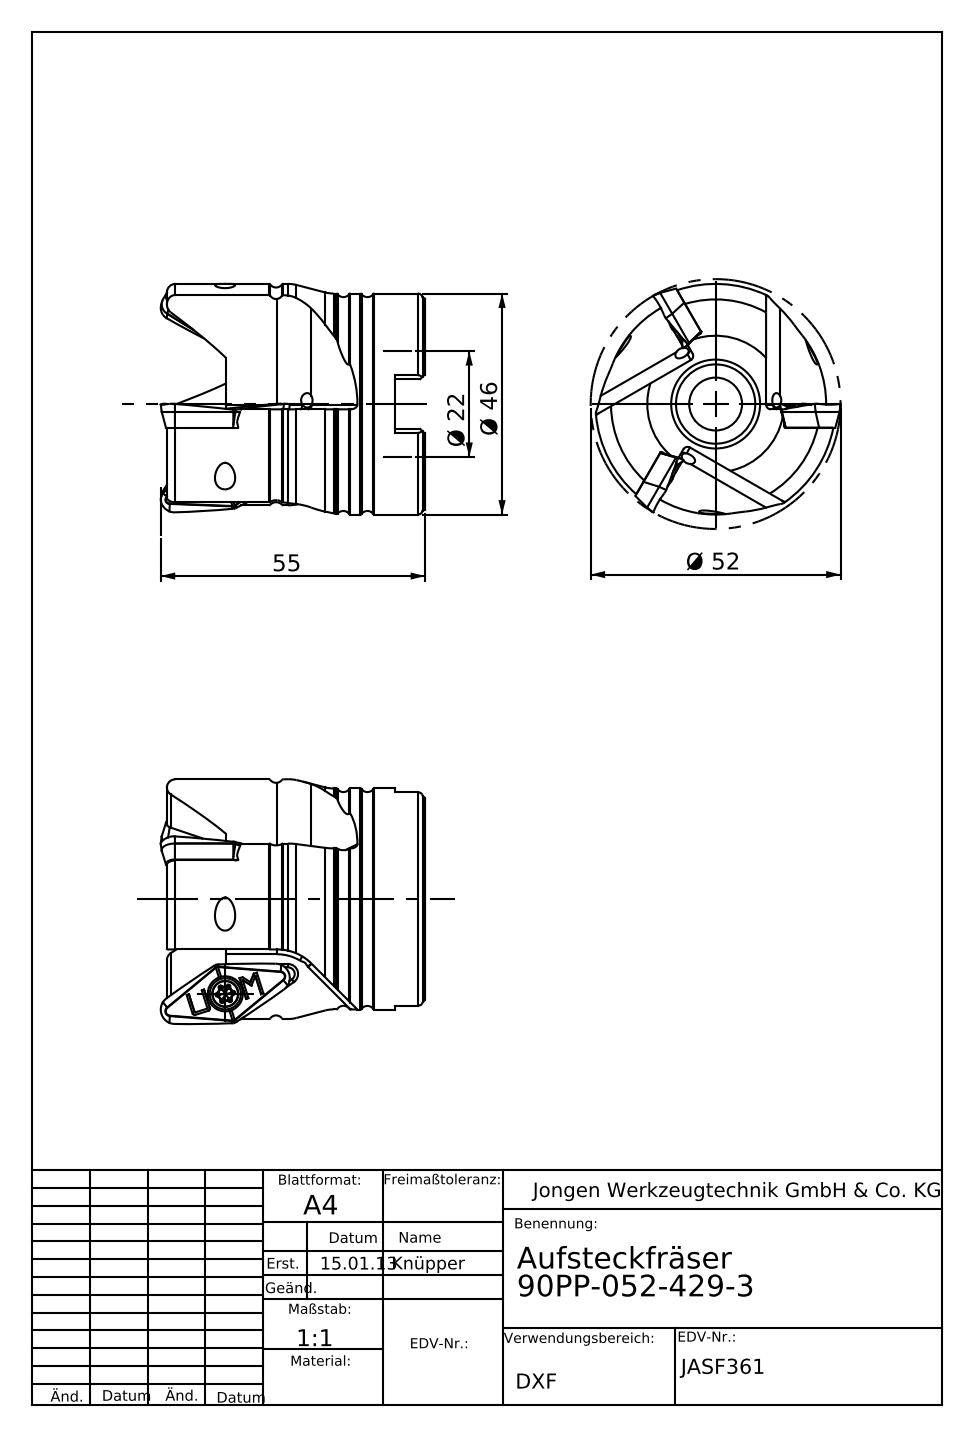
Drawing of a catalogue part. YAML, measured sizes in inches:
part_name: "90PP-052-429-3"
step_written_by: "SolidWorks 2012 (AUTOMOTIVE_DESIGN)"
units: inches
bodies: {solids: 1, faces: 167, planar: 53, cylindrical: 41, other: 73}
overall_size: [2.165, 2.05, 2.05]
volume: 4.172
surface_area: 25.95
round_holes:
  - {diameter: 0.118, count: 3}
  - {diameter: 0.433, count: 1}
  - {diameter: 0.65, count: 1}
  - {diameter: 0.86, count: 1}
  - {diameter: 0.872, count: 1}
  - {diameter: 0.878, count: 1}
round_bosses_or_shafts:
  - {diameter: 1.811, count: 1}
partial_cylinders:
  - {radius: 0.039, count: 6}
  - {radius: 0.054, count: 3}
  - {radius: 0.394, count: 3}
  - {radius: 0.984, count: 1}
face_to_face_distances: [0.248, 0.657, 0.906, 0.725, 1.383, 1.631, 0.433, 0.292, 0.95, 1.198]
